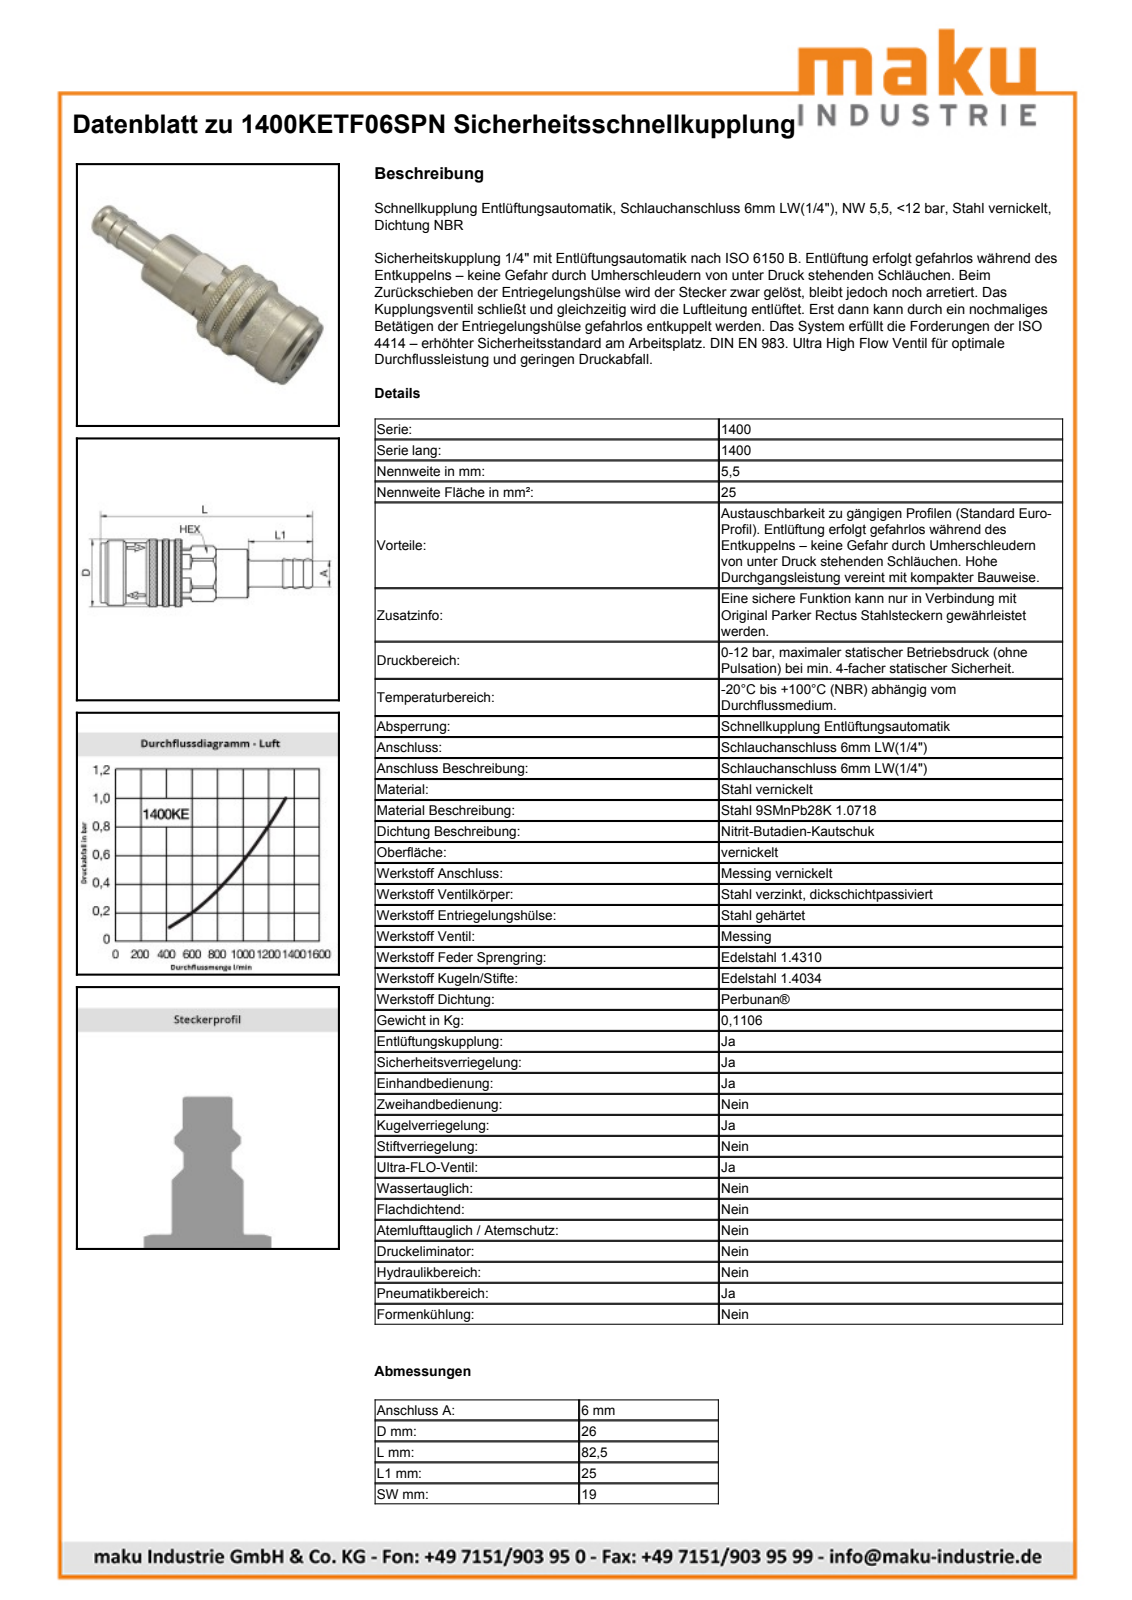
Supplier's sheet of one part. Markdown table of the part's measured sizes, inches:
| quantity | value |
| --- | --- |
| part name | 1400KETF06SPN |
| STEP written by | Autodesk Inventor 2014 (AUTOMOTIVE_DESIGN) |
| units | inches |
| bodies | 1 solid, 690 faces (305 planar, 77 cylindrical, 308 other) |
| overall size | 3.248 × 1.063 × 1.063 |
| volume | 1.466 in³ |
| surface area | 9.069 in² |
| round bosses / shafts (diameter × count) | 1.063 × 1, 1.024 × 1, 0.984 × 1, 0.925 × 1, 0.906 × 1, 0.74 × 1, 0.24 × 1 |
| partial cylindrical surfaces (radius × count) | 0.38 × 1, 0.421 × 1, 0.455 × 1 |
| main face-to-face distances | 0.748, 1.252, 1.012, 2.264, 2.252, 1.24, 0.984, 1.996, 3.236, 3.248 |
